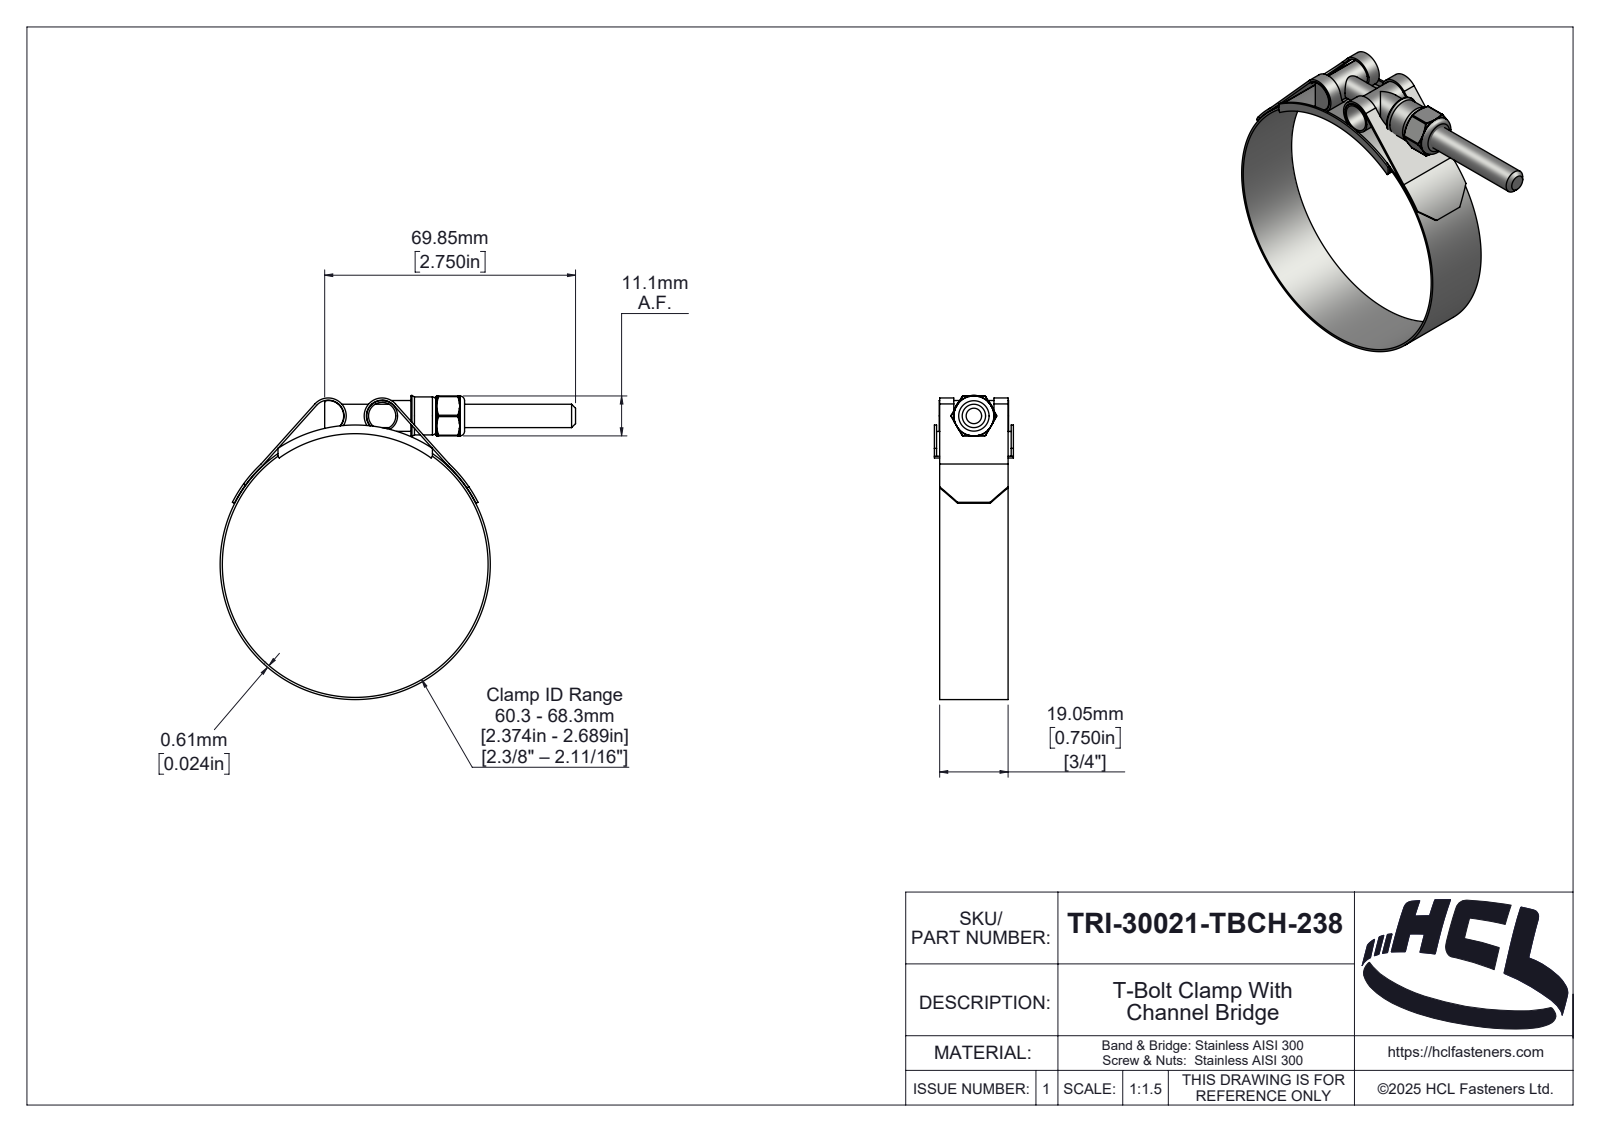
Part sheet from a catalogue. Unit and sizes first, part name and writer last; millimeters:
Units: millimetres
Overall size (bounding box): 98.96 × 84.66 × 22
Round holes (diameter × count): ⌀5.4 ×1, ⌀6.35 ×1, ⌀6.5 ×1, ⌀7.58 ×1, ⌀74 ×1
Round bosses / shafts (diameter × count): ⌀8.58 ×2, ⌀75.22 ×1, ⌀10.58 ×1
Partial cylindrical surfaces — rounded edges, fillets, slot ends (radius × count): R0.39 ×6, R0.5 ×2, R4.39 ×2, R5 ×2, R0.59 ×1, R2.42 ×1, R3.03 ×1, R3.19 ×1
Main face-to-face distances: 0.61, 1.47, 20.53, 19.06, 21.39, 0.86, 19.92, 0.74, 22, 11.11
Hole centre spacings: 42
Volume: 8 344 mm³ · Surface area: 18 551 mm²
Bodies: 6 solids, 330 faces (46 planar, 122 cylindrical, 162 other)
Part name (STEP PRODUCT): TRI-30021-TBCH-238
STEP written by: SolidWorks 2025 (AUTOMOTIVE_DESIGN)
